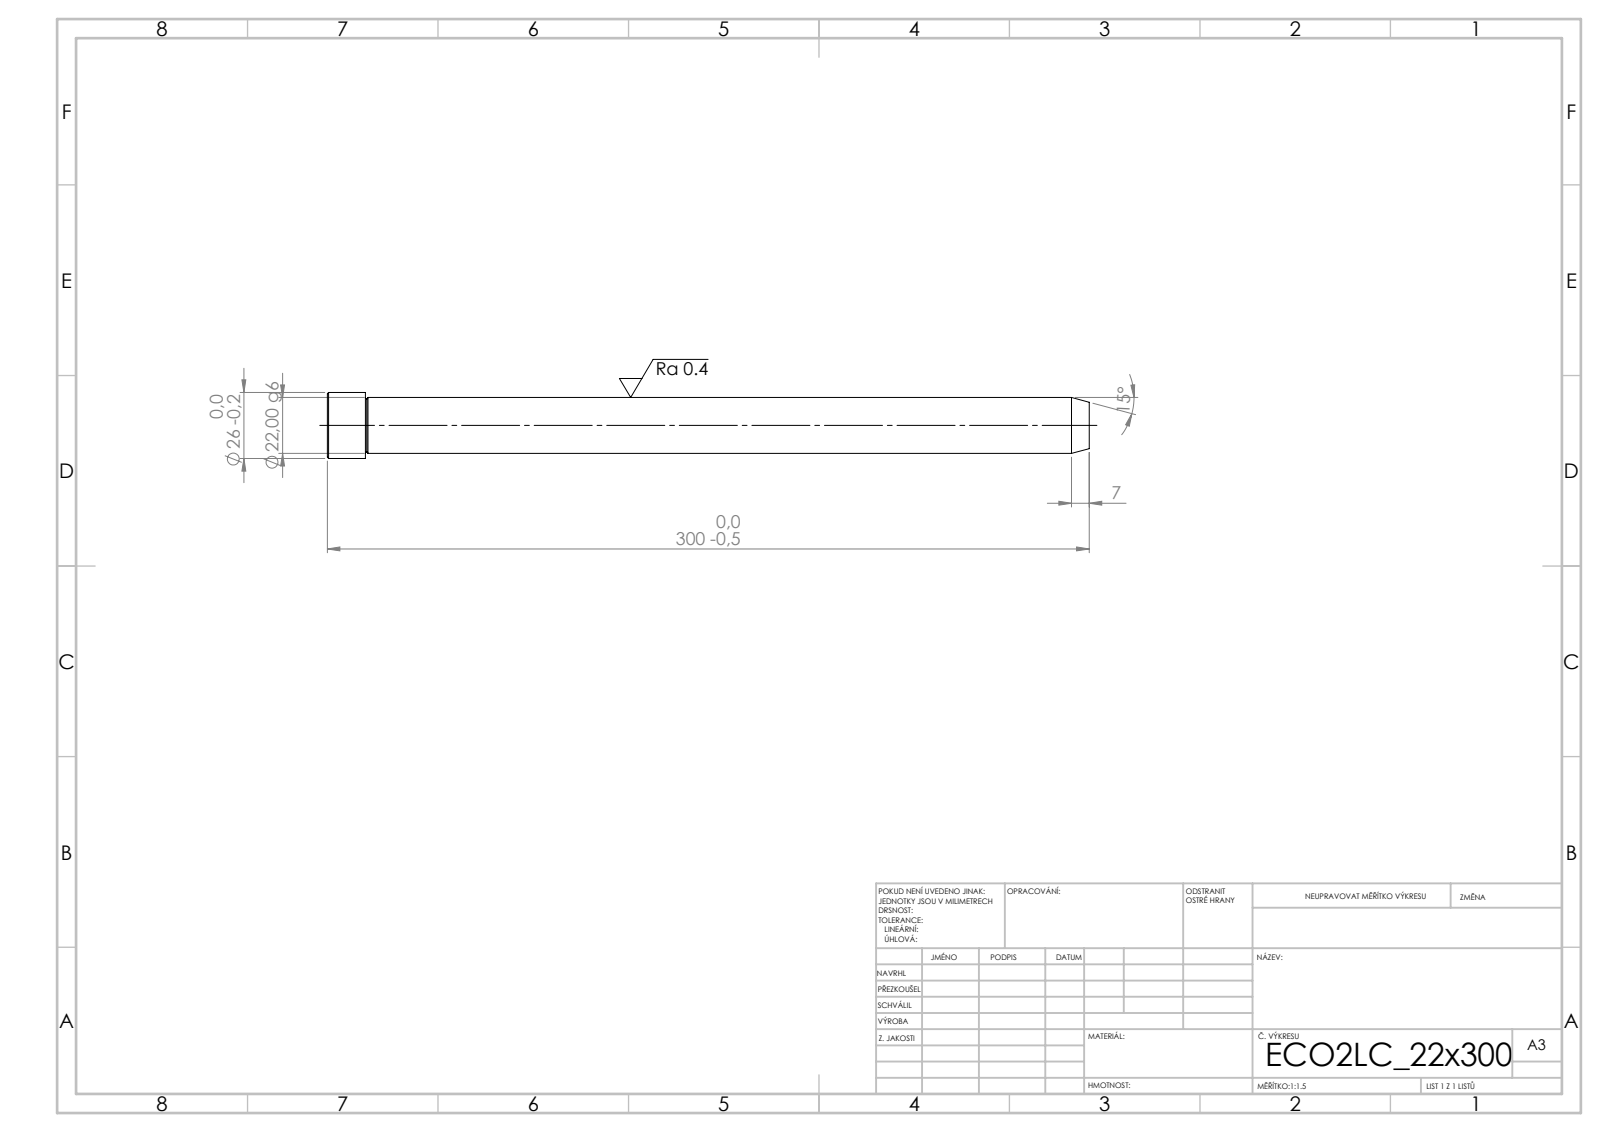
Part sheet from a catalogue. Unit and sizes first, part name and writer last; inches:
Units: inches
Overall size (bounding box): 11.811 × 1.024 × 1.024
Round bosses / shafts (diameter × count): ⌀1.024 ×1, ⌀0.866 ×1
Main face-to-face distances: 11.811, 11.22, 0.591
Volume: 7.069 in³ · Surface area: 33.87 in²
Bodies: 1 solid, 15 faces (3 planar, 4 cylindrical, 8 other)
STEP written by: SolidWorks 2019 (CONFIG_CONTROL_DESIGN)
